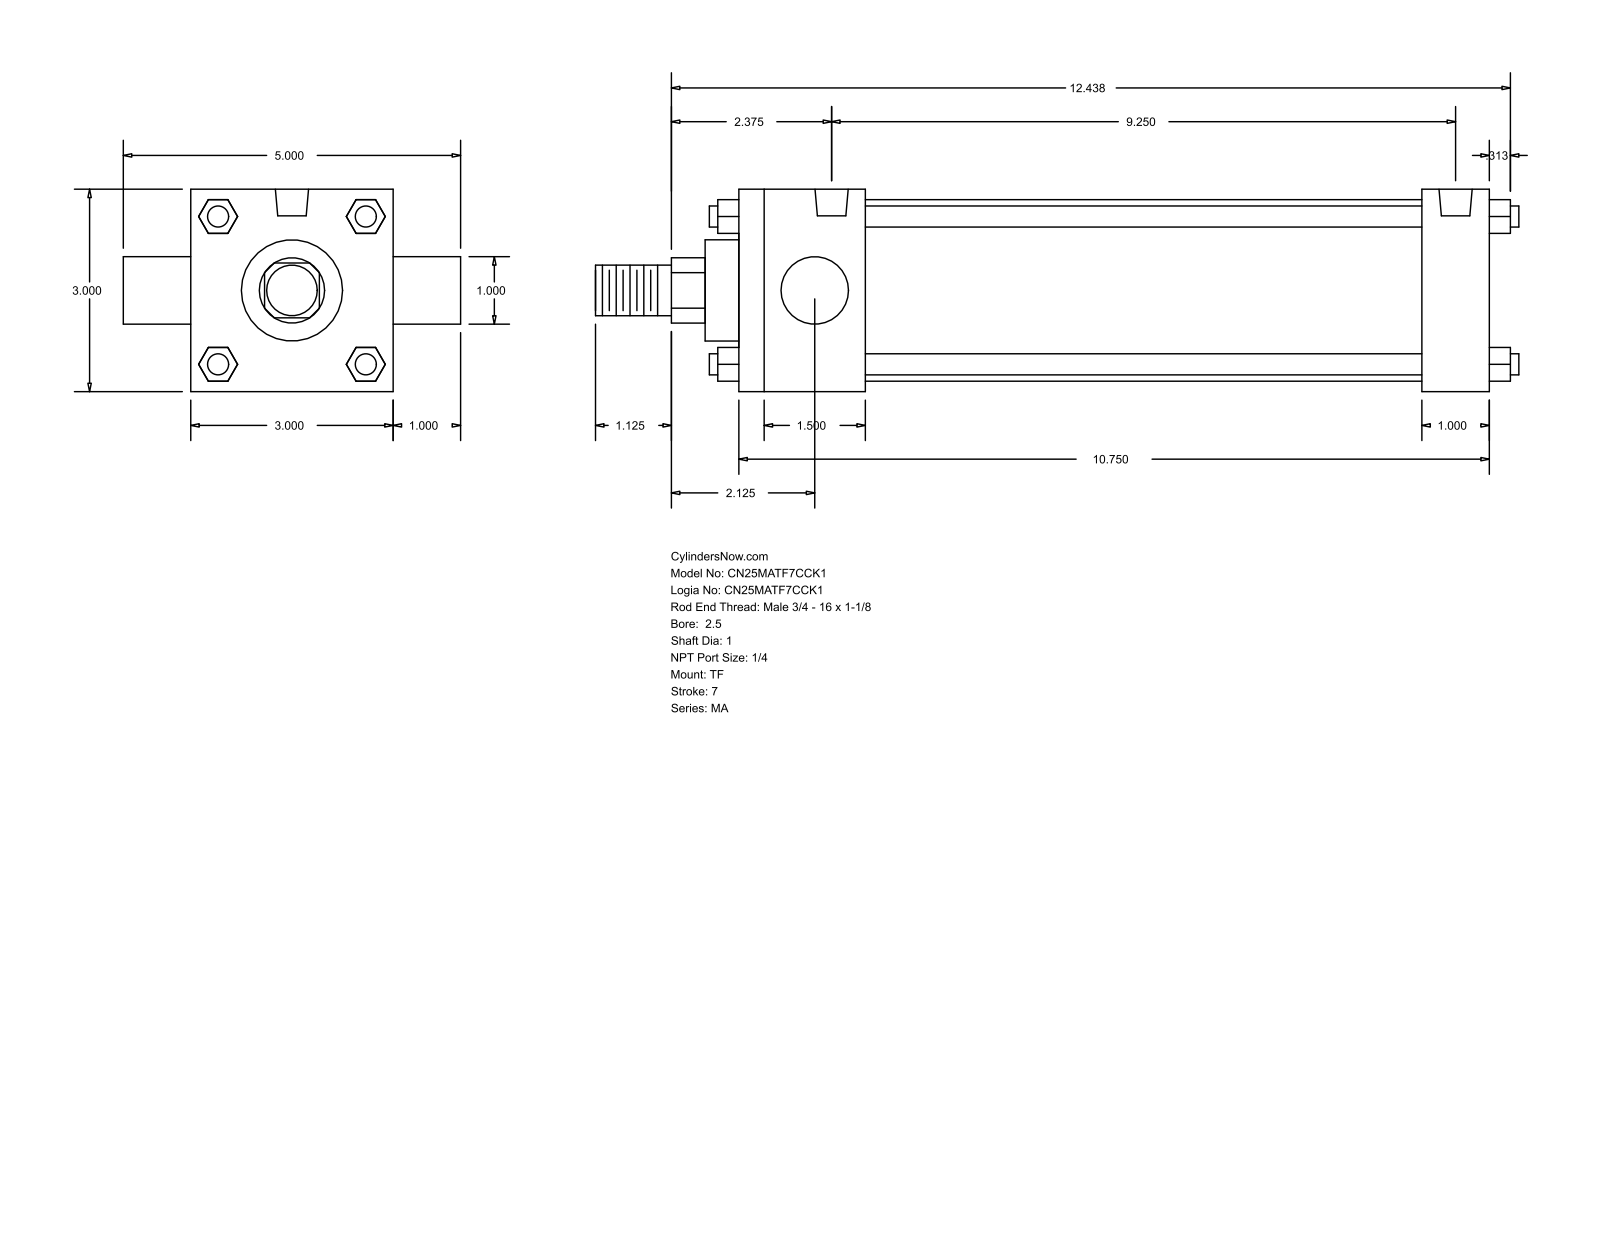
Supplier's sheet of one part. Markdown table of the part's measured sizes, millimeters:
| quantity | value |
| --- | --- |
| part name | MA_TF__0250_1 |
| STEP written by | GSSL Pune (CONFIG_CONTROL_DESIGN) |
| units | millimeters |
| bodies | 0 solids, 120 faces (92 planar, 28 cylindrical, 0 other) |
| overall size | 347.66 × 127 × 76.2 |
| round holes (diameter × count) | 7.94 × 3, 12.49 × 2 |
| round bosses / shafts (diameter × count) | 7.94 × 4, 25.4 × 2, 68.33 × 1, 38.1 × 1, 19.05 × 1 |
| partial cylindrical surfaces (radius × count) | 12.29 × 1 |
| main face-to-face distances | 76.2, 282.58, 12.7, 47.63, 257.17, 209.54, 234.95, 25.41, 101.6, 25.4 |
| hole center spacings | 234.94 |
